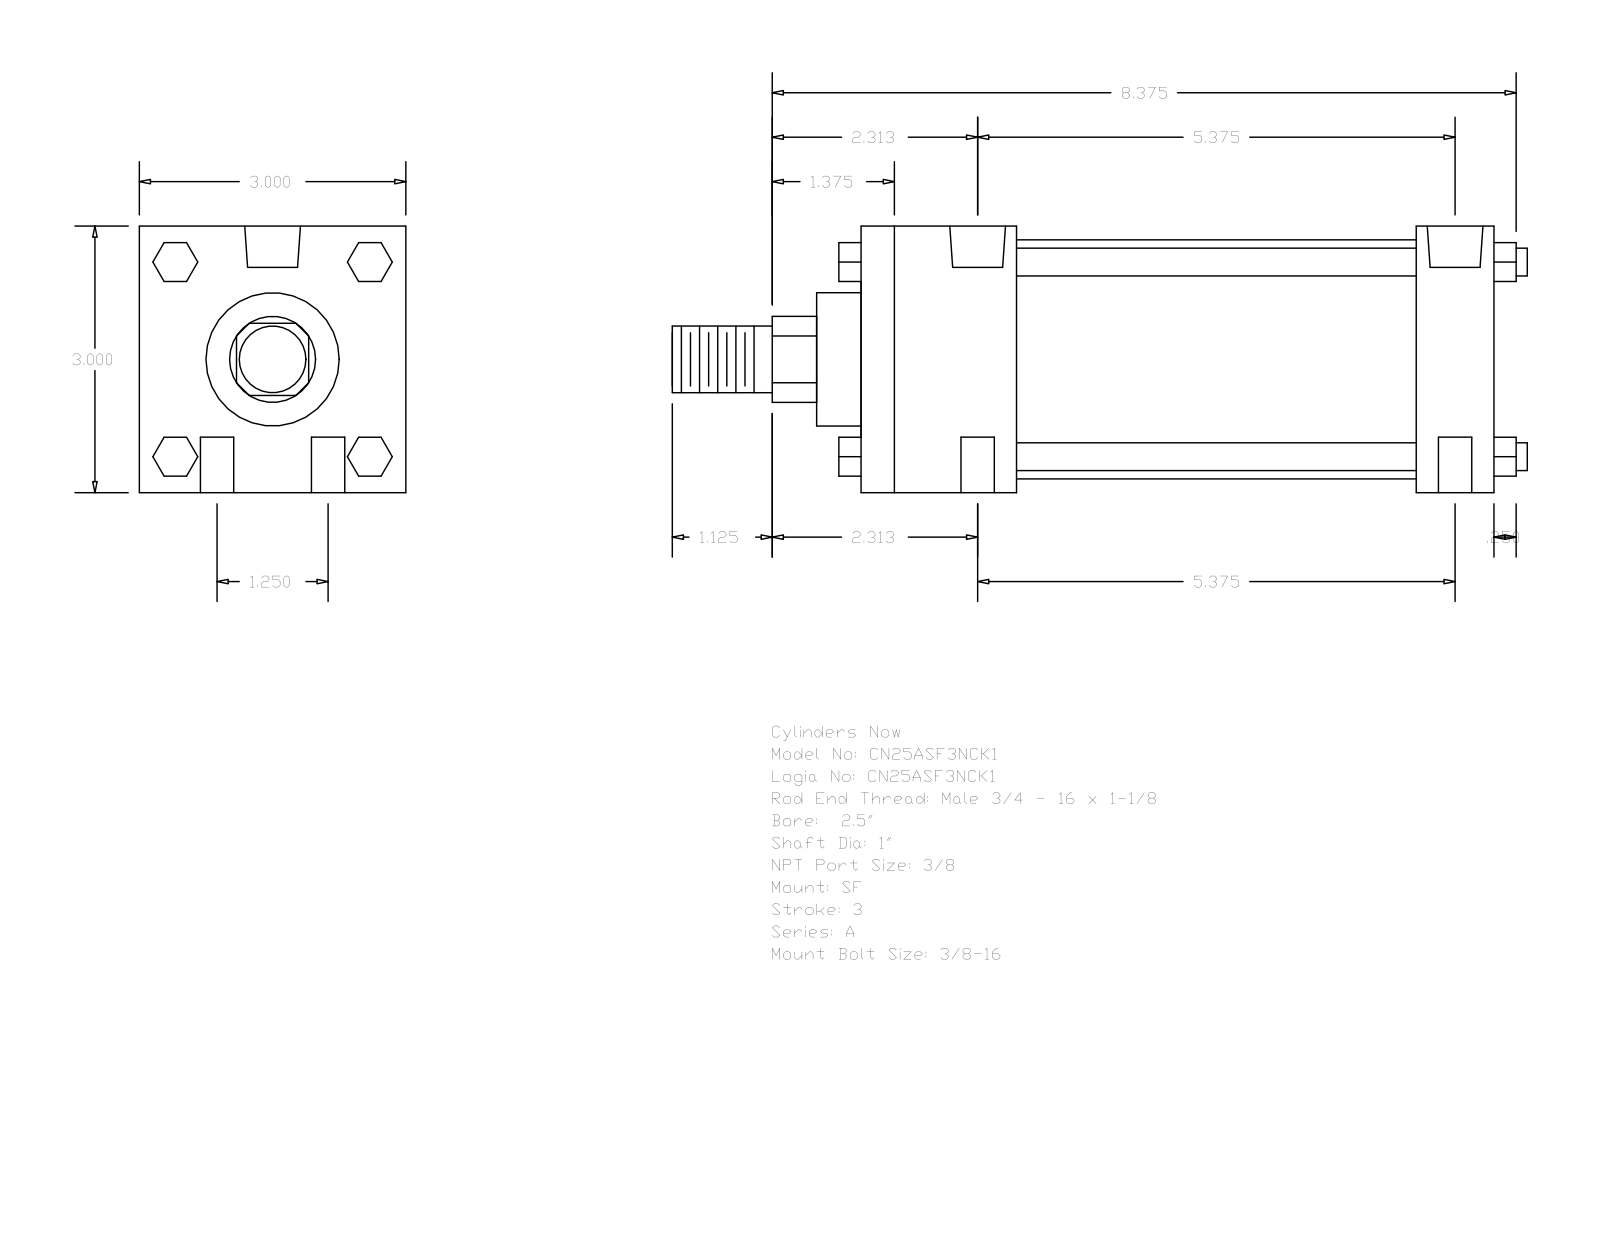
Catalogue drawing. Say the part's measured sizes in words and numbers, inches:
The part is named "A_SF__0250_1". Its 3-D file was written by "GSSL Pune (CONFIG_CONTROL_DESIGN)". It is 0 solids with 124 faces: 94 planar, 30 cylindrical and 0 other. Overall it measures 9.625 by 3 by 3 inches. Round holes: 4 of diameter 0.375, 2 of diameter 0.219, 2 of diameter 0.627. Round bosses or shafts: 4 of diameter 0.313, 1 of diameter 2.69, 1 of diameter 1.5, 1 of diameter 1, 1 of diameter 0.75. Partial cylindrical surfaces (rounded edges, fillets, slot ends): 1 of radius 0.484. The main face-to-face distances are 3, 7.125, 6.25, 0.875, 1.75, 4.5, 5.375, 0.5, 0.437, 2.25. The hole center spacings are 0.625, 5.411, 5.375, 1.25, 5.519, 5.562.
